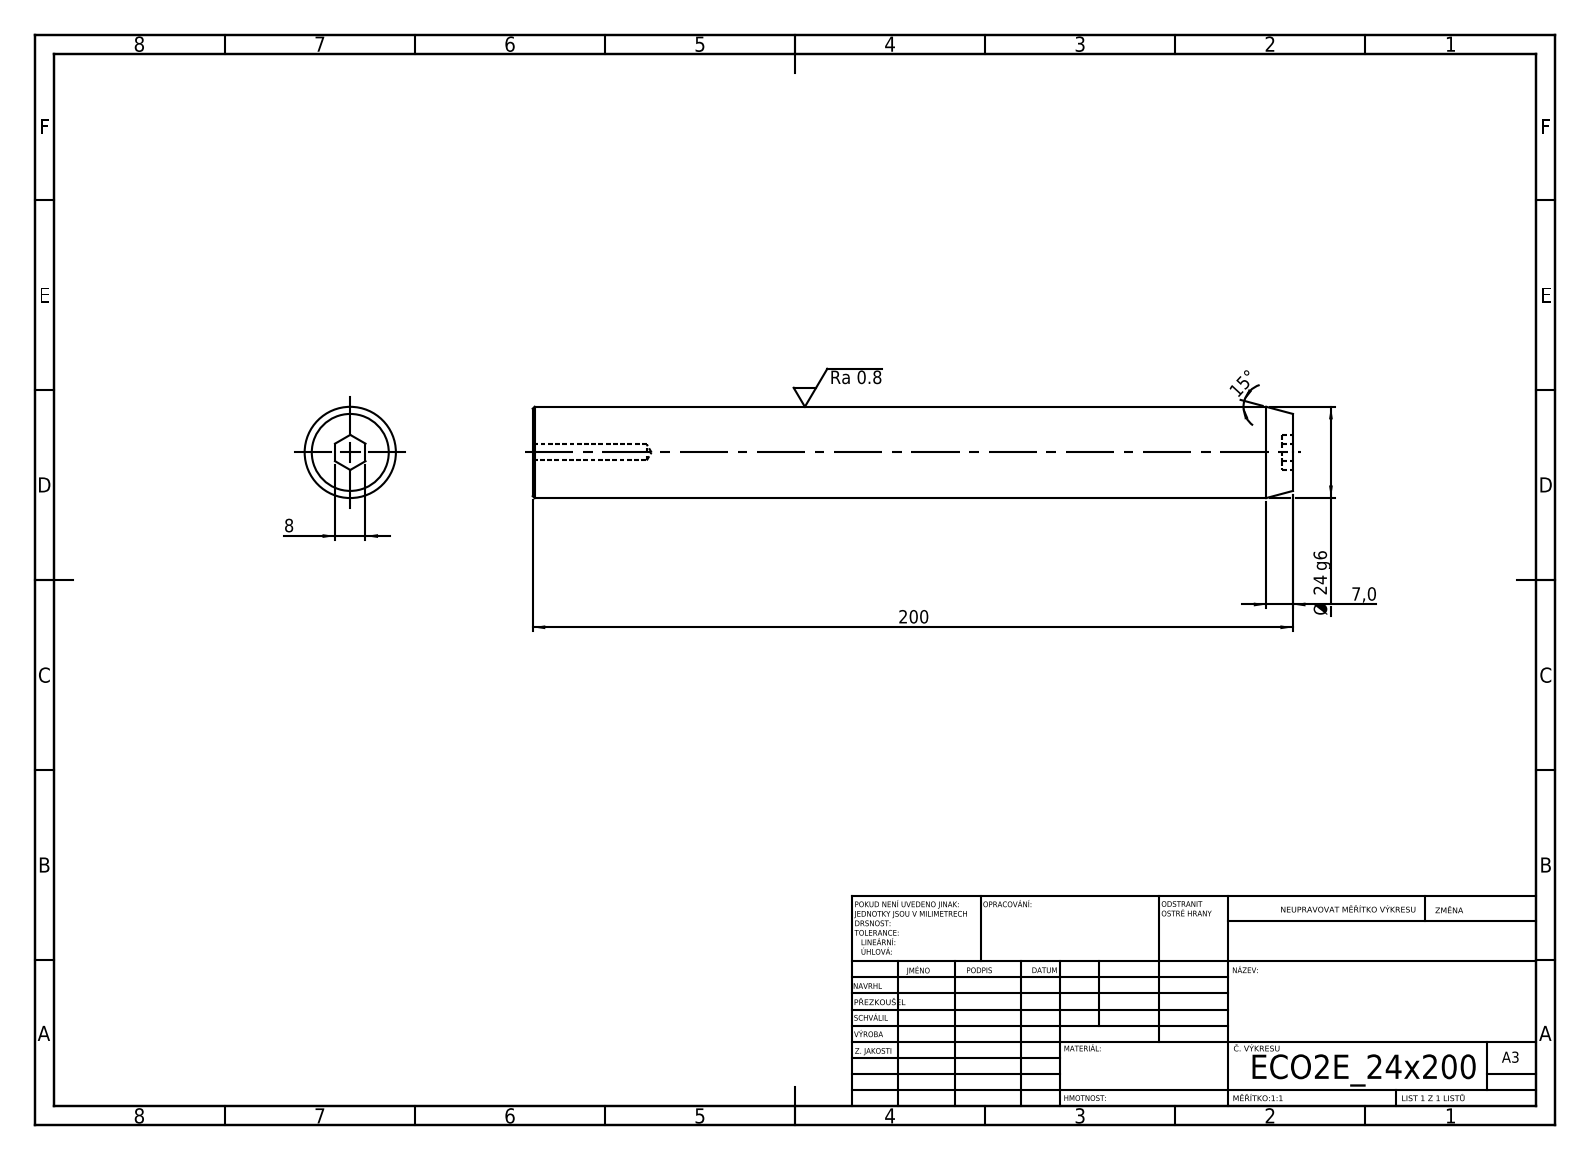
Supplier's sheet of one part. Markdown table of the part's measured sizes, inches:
| quantity | value |
| --- | --- |
| STEP written by | SolidWorks 2019 (CONFIG_CONTROL_DESIGN) |
| units | inches |
| bodies | 1 solid, 19 faces (9 planar, 4 cylindrical, 6 other) |
| overall size | 7.874 × 0.945 × 0.945 |
| volume | 5.457 in³ |
| surface area | 25.24 in² |
| round holes (diameter × count) | 0.165 × 1 |
| round bosses / shafts (diameter × count) | 0.945 × 1 |
| main face-to-face distances | 7.874, 0.11, 7.764, 0.315 |
